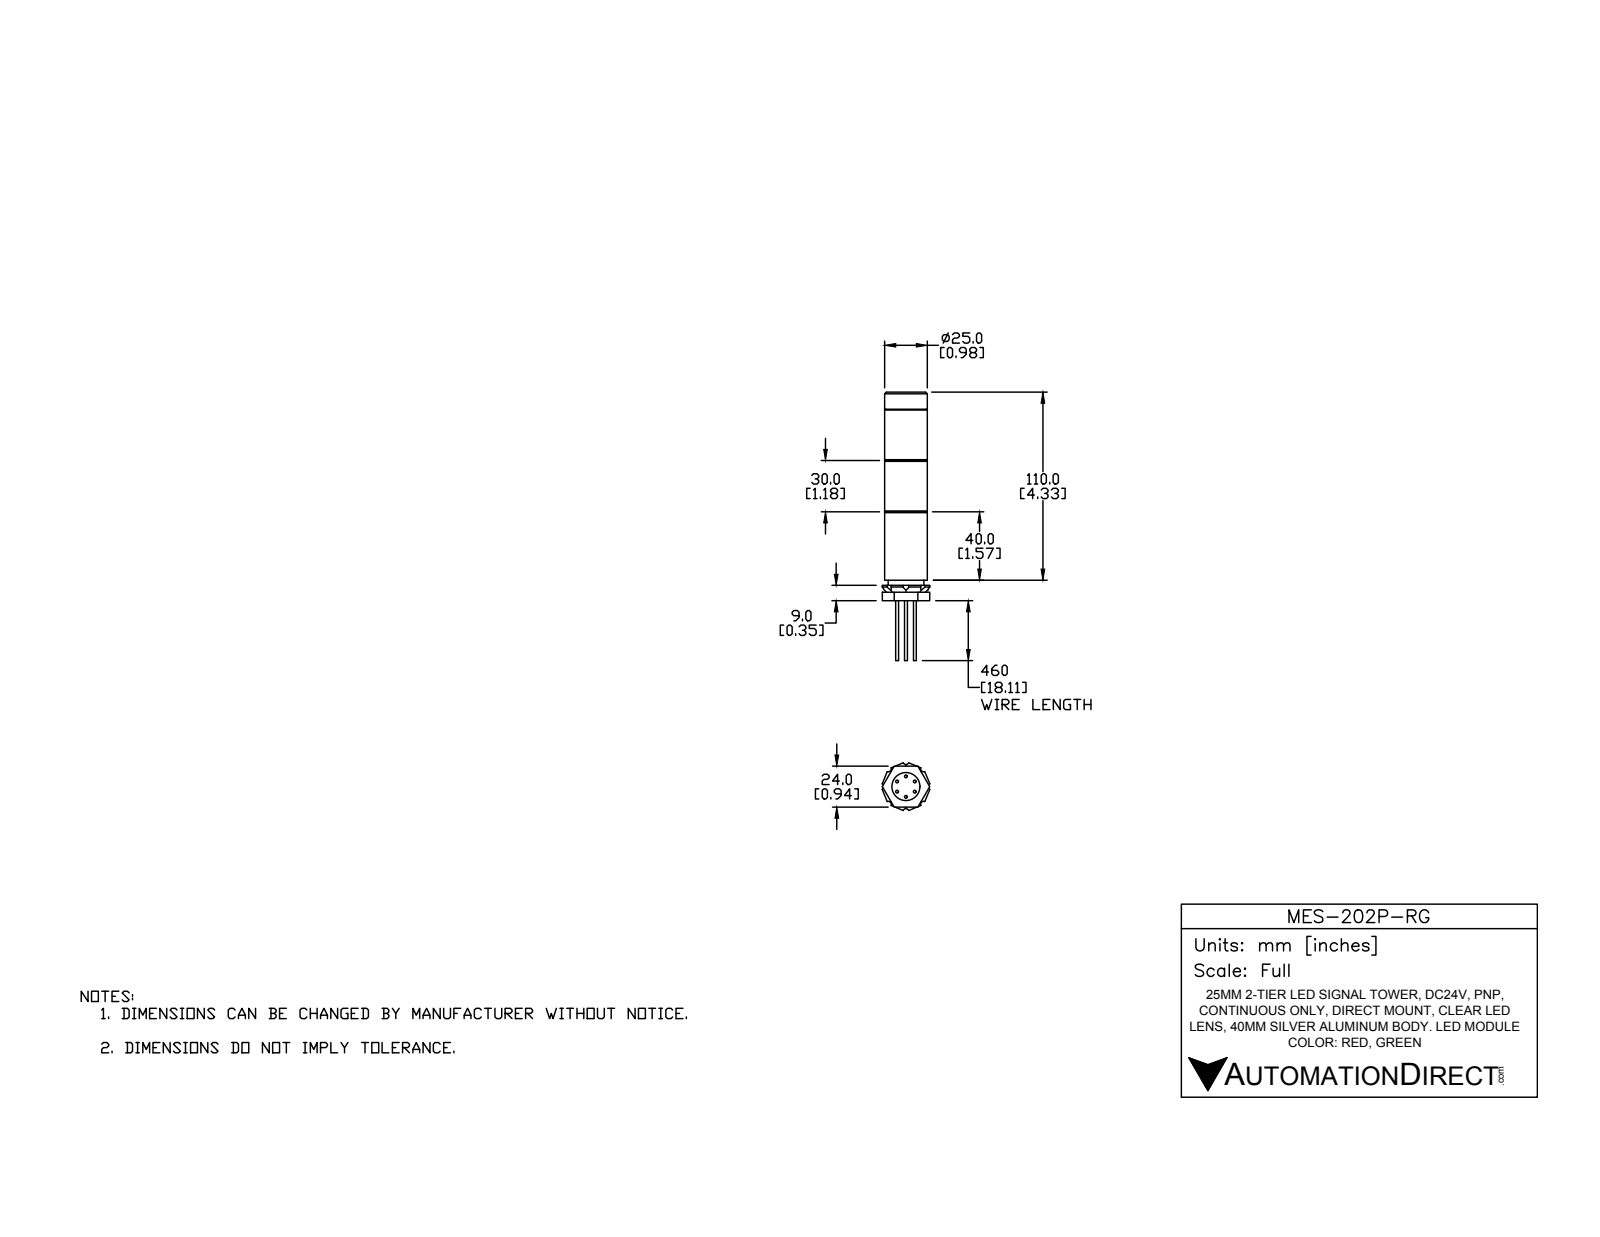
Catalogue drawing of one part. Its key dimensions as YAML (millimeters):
part_name: "MES-202P-RG"
step_written_by: "SolidWorks 2016 (AUTOMOTIVE_DESIGN)"
units: millimeters
bodies: {solids: 13, faces: 140, planar: 73, cylindrical: 49, other: 18}
overall_size: [157, 27.89, 27.89]
volume: 48359
surface_area: 21968
round_holes:
  - {diameter: 3.2, count: 1}
  - {diameter: 7.7, count: 1}
  - {diameter: 16.4, count: 1}
  - {diameter: 18, count: 1}
  - {diameter: 20.7, count: 1}
  - {diameter: 21, count: 1}
round_bosses_or_shafts:
  - {diameter: 1.7, count: 6}
  - {diameter: 25, count: 1}
  - {diameter: 20.9, count: 1}
  - {diameter: 16, count: 1}
  - {diameter: 5, count: 1}
partial_cylinders:
  - {radius: 1.75, count: 8}
face_to_face_distances: [30, 60, 40, 7, 77, 70, 37, 67, 10, 45]
